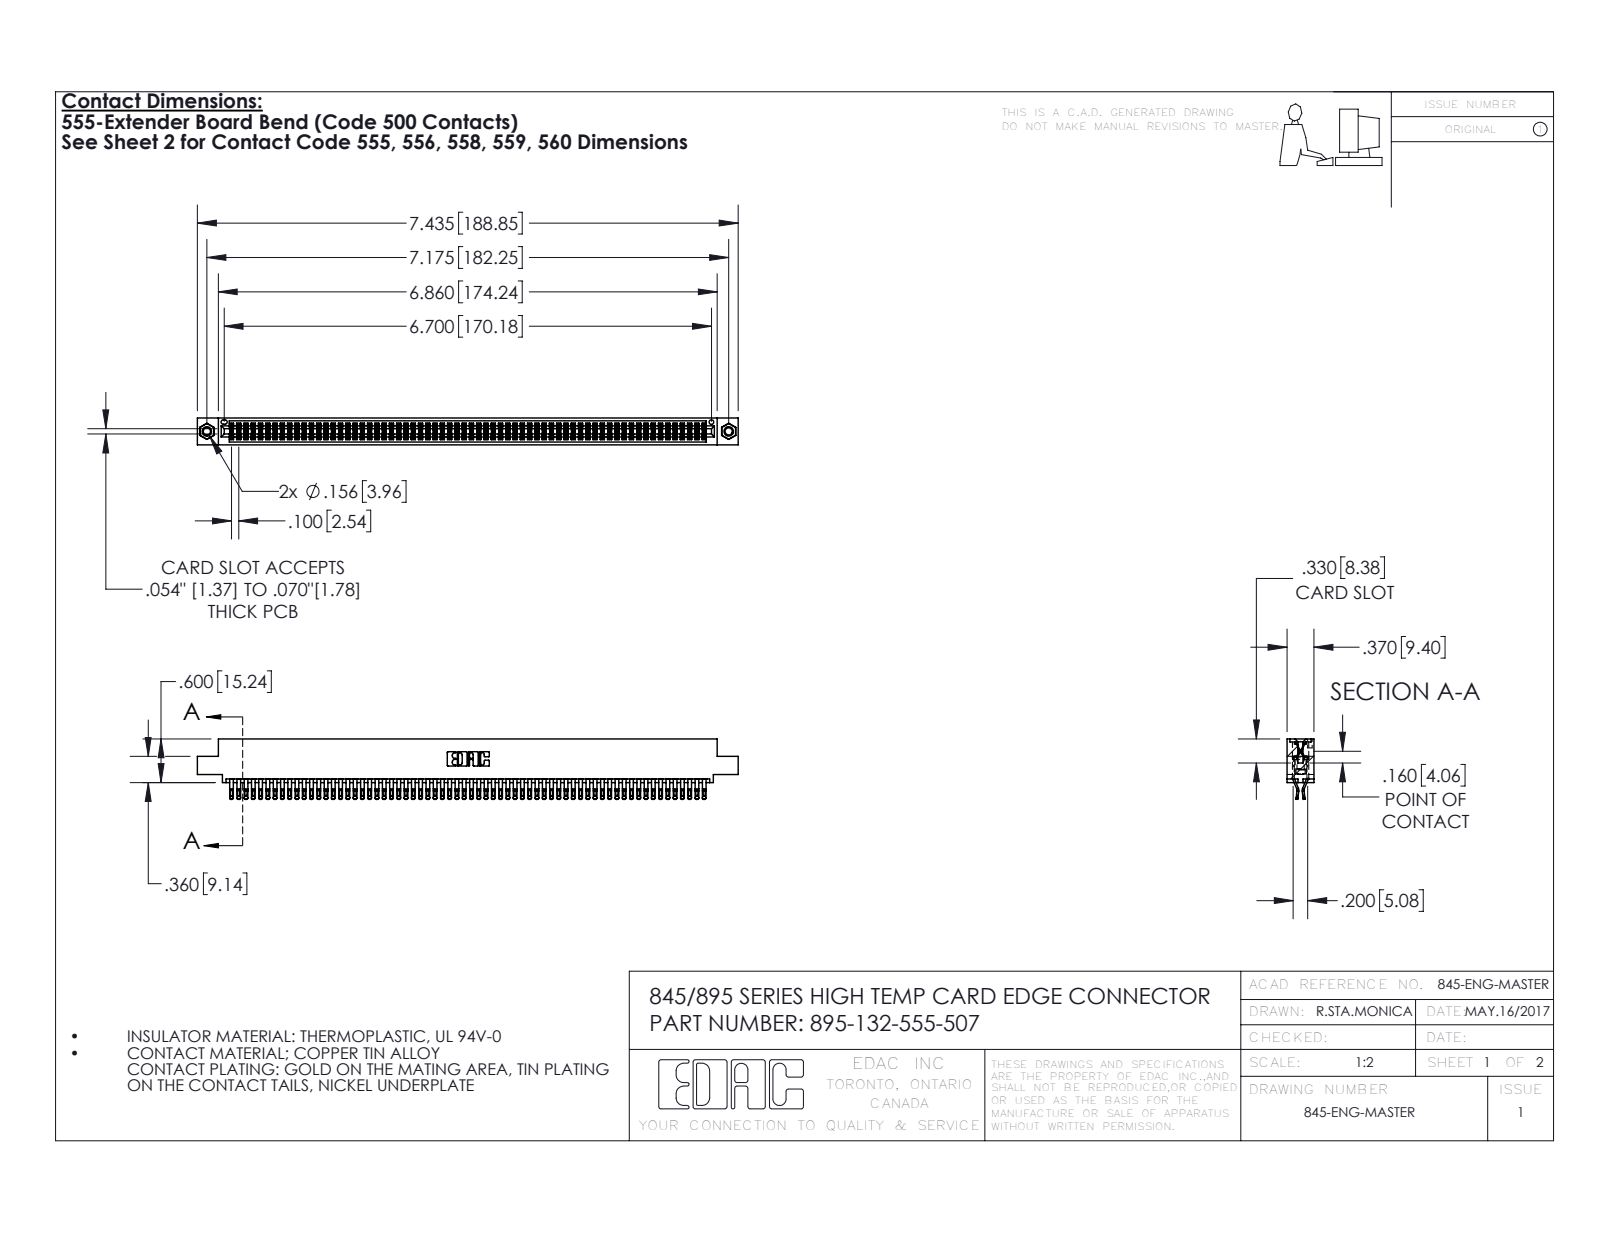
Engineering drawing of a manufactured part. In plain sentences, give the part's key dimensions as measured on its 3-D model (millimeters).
The part is named "395-132-555-507; 345-292-001_555 Tail; 345-250-001_345-250-005-103; 345 Part_0.110 Offset - 0.156 Dia-TI". Its 3-D file was written by "SolidWorks 2016 (CONFIG_CONTROL_DESIGN)". It is 135 solids with 7582 faces: 4208 planar, 3358 cylindrical and 16 other. Overall it measures 188.8 by 21.1 by 9.4 millimeters. Its volume is 18 860 cubic millimeters and its surface area 29 800 square millimeters. Round holes: 2 of diameter 2.5, 2 of diameter 3.2, 2 of diameter 4, 1 of diameter 1.6. Round bosses or shafts: 2 of diameter 3.9. Partial cylindrical surfaces (rounded edges, fillets, slot ends): 330 of radius 0.4, 264 of radius 0.5, 198 of radius 0.2, 22 of radius 0.3, 6 of radius 0.2, 6 of radius 0.8, 3 of radius 0.7, 2 of radius 0.3. The main face-to-face distances are 1.8, 7.6, 0.6, 9.4, 5.1, 2.5, 6.9, 5.7, 4.4, 3.8. The hole center spacings are 6.9, 176.3, 182.2.
